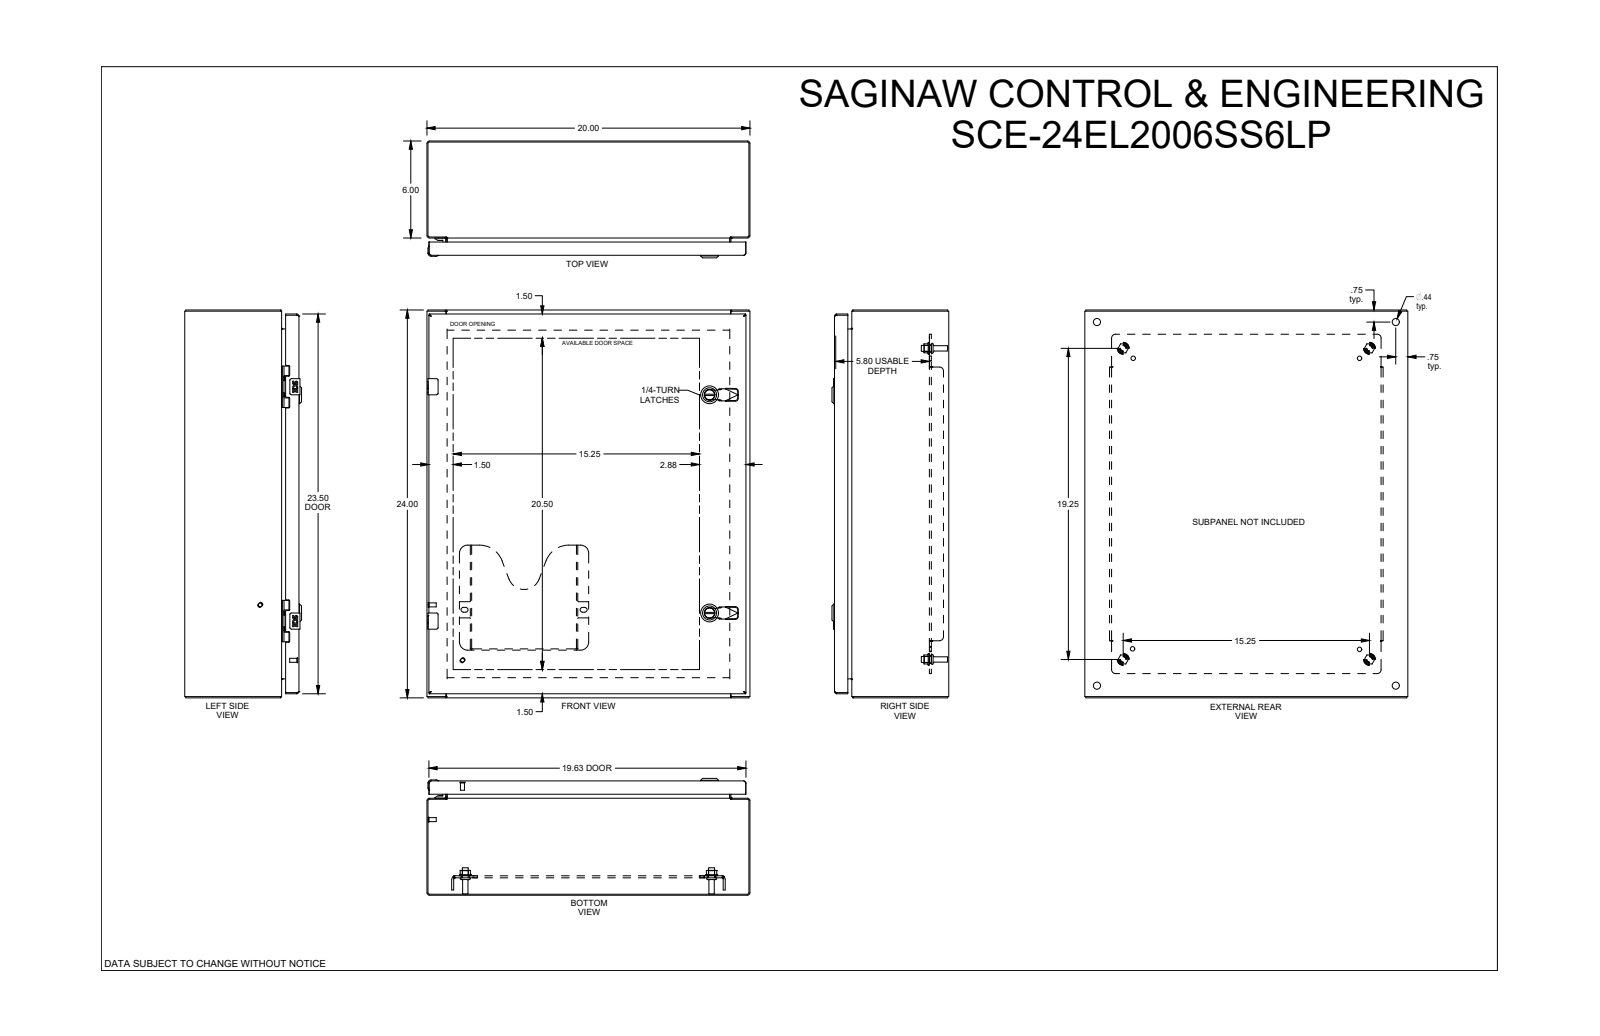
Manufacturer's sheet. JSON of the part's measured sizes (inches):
{"part_name": "SCE-24EL2006LP", "step_written_by": "SolidWorks 2021 (AUTOMOTIVE_DESIGN)", "units": "inches", "bodies": {"solids": 45, "faces": 2787, "planar": 1089, "cylindrical": 840, "other": 858}, "overall_size": [24, 20, 7.23], "volume_in3": 186.5, "surface_area_in2": 4472, "round_holes": [[0.172, 4], [0.205, 4], [0.244, 4], [0.266, 4], [0.281, 4], [0.367, 4], [0.375, 4], [0.437, 4], [0.5, 4], [0.04, 2], [0.188, 2], [0.197, 2]], "round_bosses_or_shafts": [[0.17, 6], [0.366, 4], [0.332, 4], [0.25, 4], [0.248, 4], [0.24, 4], [0.196, 3], [1.102, 2]], "partial_cylinders_radius": [[0.012, 56], [0.01, 28], [0.015, 24], [0.02, 20], [0.04, 17], [0.06, 13], [0.029, 12], [0.1, 12]], "face_to_face_distances": [0.075, 0.06, 7.073, 6.998, 7.013, 6.938, 1, 0.125, 1.2, 1.125], "hole_center_spacings": [0.985, 14.5, 0.02, 0.493, 0.494, 0.875, 2.298, 4.493]}
